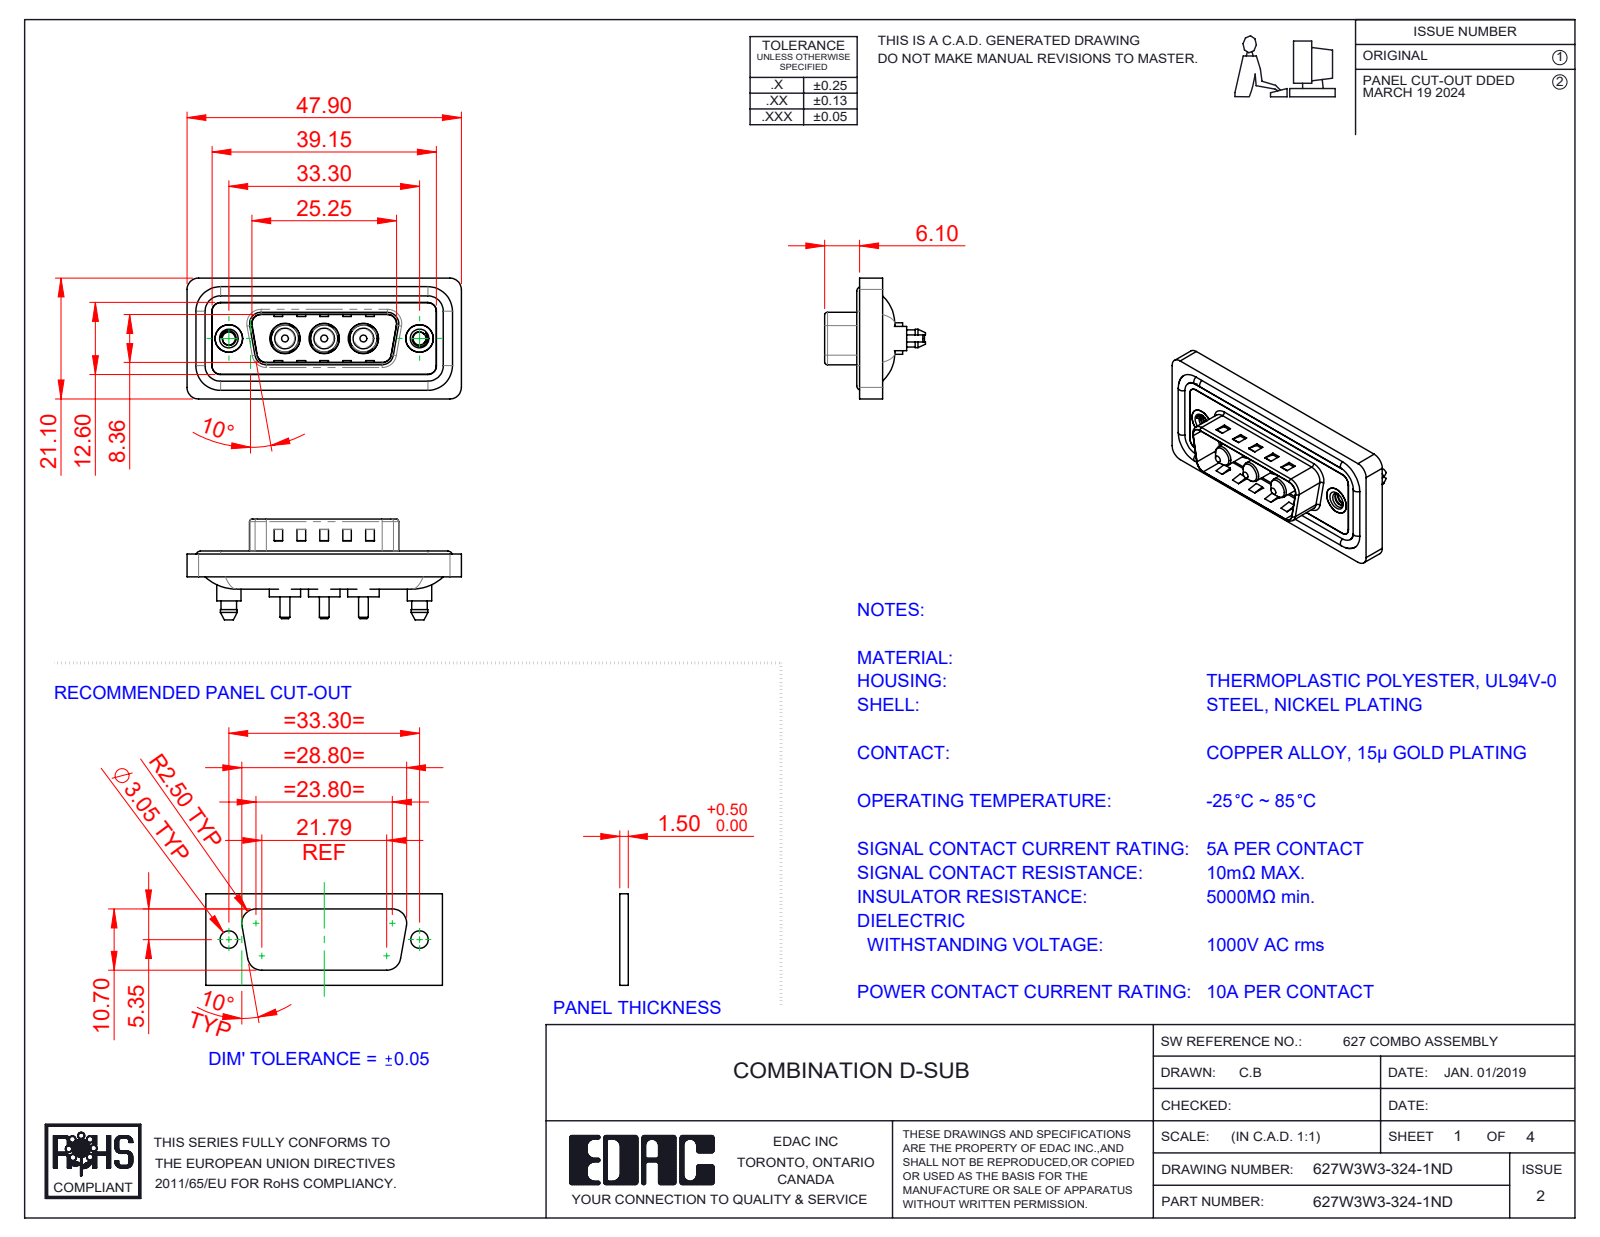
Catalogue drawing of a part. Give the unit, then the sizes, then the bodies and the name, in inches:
Units: inches
Overall size (bounding box): 1.886 × 0.831 × 0.693
Round holes (diameter × count): ⌀0.191 ×3, ⌀0.209 ×3, ⌀0.089 ×2, ⌀0.157 ×2, ⌀0.189 ×2, ⌀0.197 ×2
Round bosses / shafts (diameter × count): ⌀0.063 ×4, ⌀0.217 ×3, ⌀0.205 ×3, ⌀0.187 ×3, ⌀0.148 ×3, ⌀0.142 ×3, ⌀0.067 ×3, ⌀0.213 ×2
Partial cylindrical surfaces — rounded edges, fillets, slot ends (radius × count): R0.059 ×28, R0.079 ×20, R0.063 ×10, R0.02 ×8, R0.01 ×4, R0.024 ×4, R0.026 ×4, R0.035 ×4
Main face-to-face distances: 0.016, 0.059, 0.043, 0.063, 0.02, 0.122, 0.114, 0.157, 0.028, 0.032
Hole centre spacings: 0.27, 0.386, 0.656, 0.925, 0.539, 1.311
Volume: 0.346 in³ · Surface area: 14.03 in²
Bodies: 13 solids, 622 faces (223 planar, 281 cylindrical, 118 other)
Part name (STEP PRODUCT): 627Combo Shell Front_15 Contacts; Power Pin_10A S; 627Combo Waterproof Housing_15 Contacts; 627Combo Housing_3W3 (+4 more)
STEP written by: SolidWorks 2023 (CONFIG_CONTROL_DESIGN)
